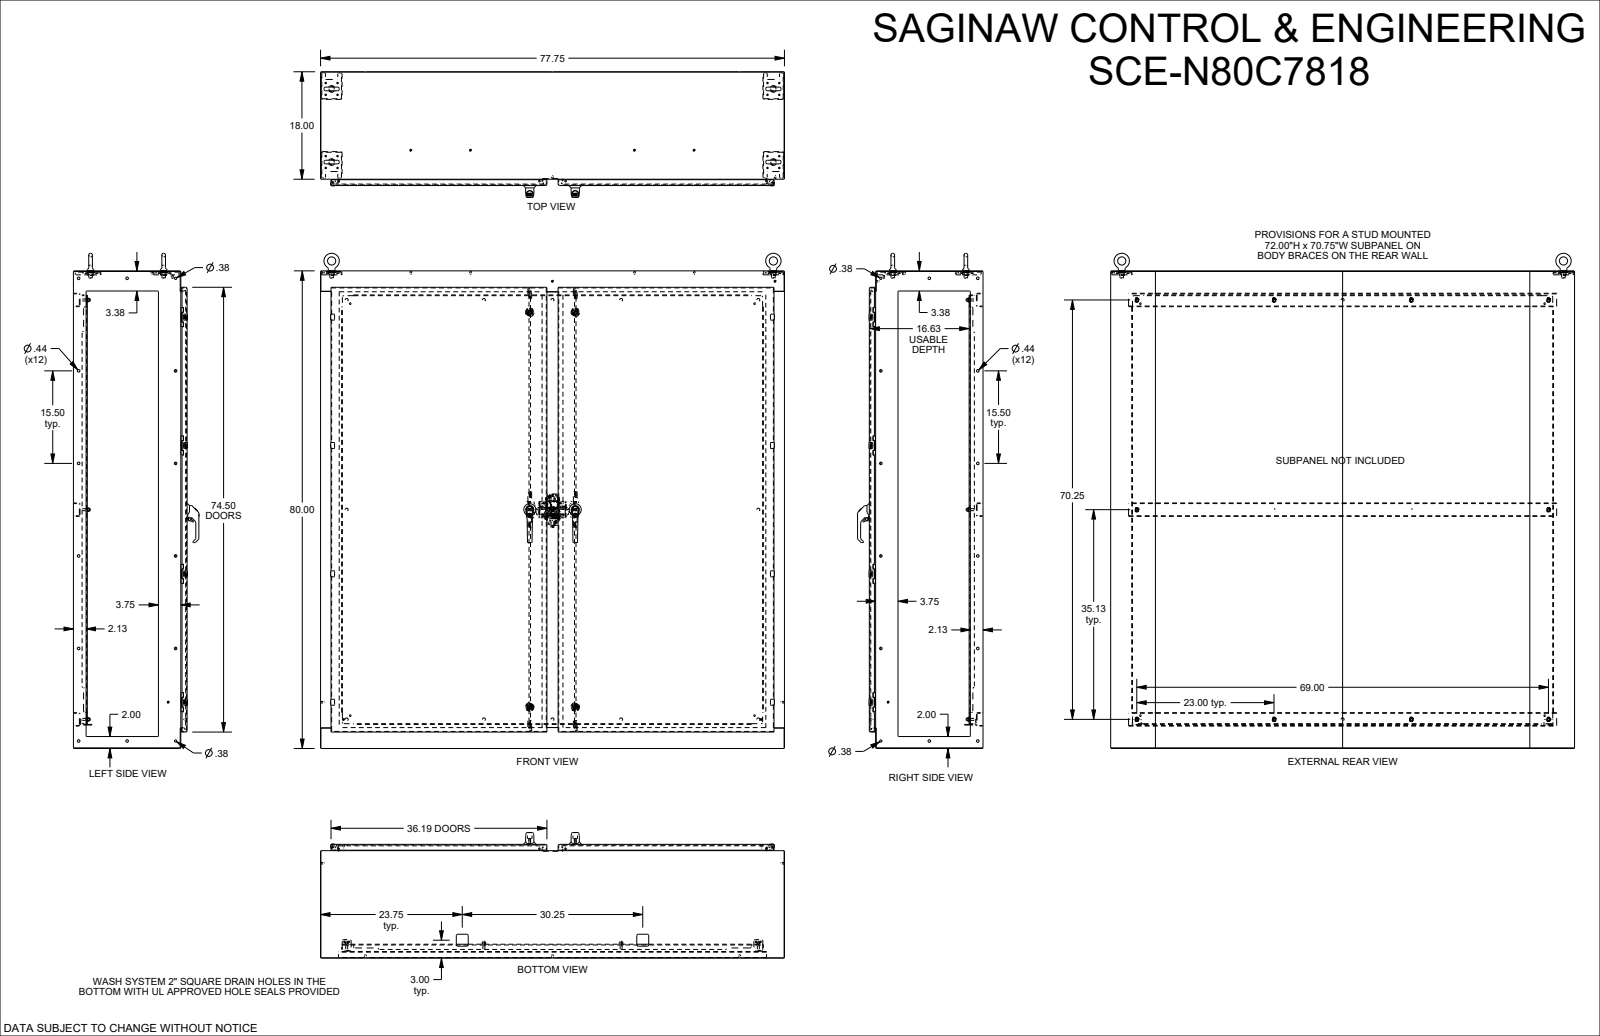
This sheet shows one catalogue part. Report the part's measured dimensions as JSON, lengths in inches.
{"part_name": "SCE-N80C7818", "step_written_by": "SolidWorks 2023 (AUTOMOTIVE_DESIGN)", "units": "inches", "bodies": {"solids": 50, "faces": 8109, "planar": 3270, "cylindrical": 2701, "other": 2138}, "overall_size": [82.945, 77.75, 21.046], "volume_in3": 2027, "surface_area_in2": 38415, "round_holes": [[0.25, 20], [0.375, 18], [0.205, 16], [0.244, 16], [0.437, 12], [0.04, 8], [0.17, 8], [0.218, 8], [0.256, 4], [0.343, 4], [0.344, 4], [0.36, 4]], "round_bosses_or_shafts": [[0.17, 24], [0.25, 20], [0.24, 16], [0.196, 10], [1.4, 4], [1.173, 4], [0.6, 4], [0.341, 4]], "partial_cylinders_radius": [[0.03, 200], [0.015, 166], [0.125, 100], [0.02, 72], [0.02, 48], [0.039, 42], [0.04, 40], [0.167, 38]], "face_to_face_distances": [0.104, 18.954, 19.058, 18.85, 79.896, 17.896, 1.058, 17.792, 1.162, 80], "hole_center_spacings": [21.5, 1.979, 1.4, 15.5, 22.457, 43, 31, 35.001]}
